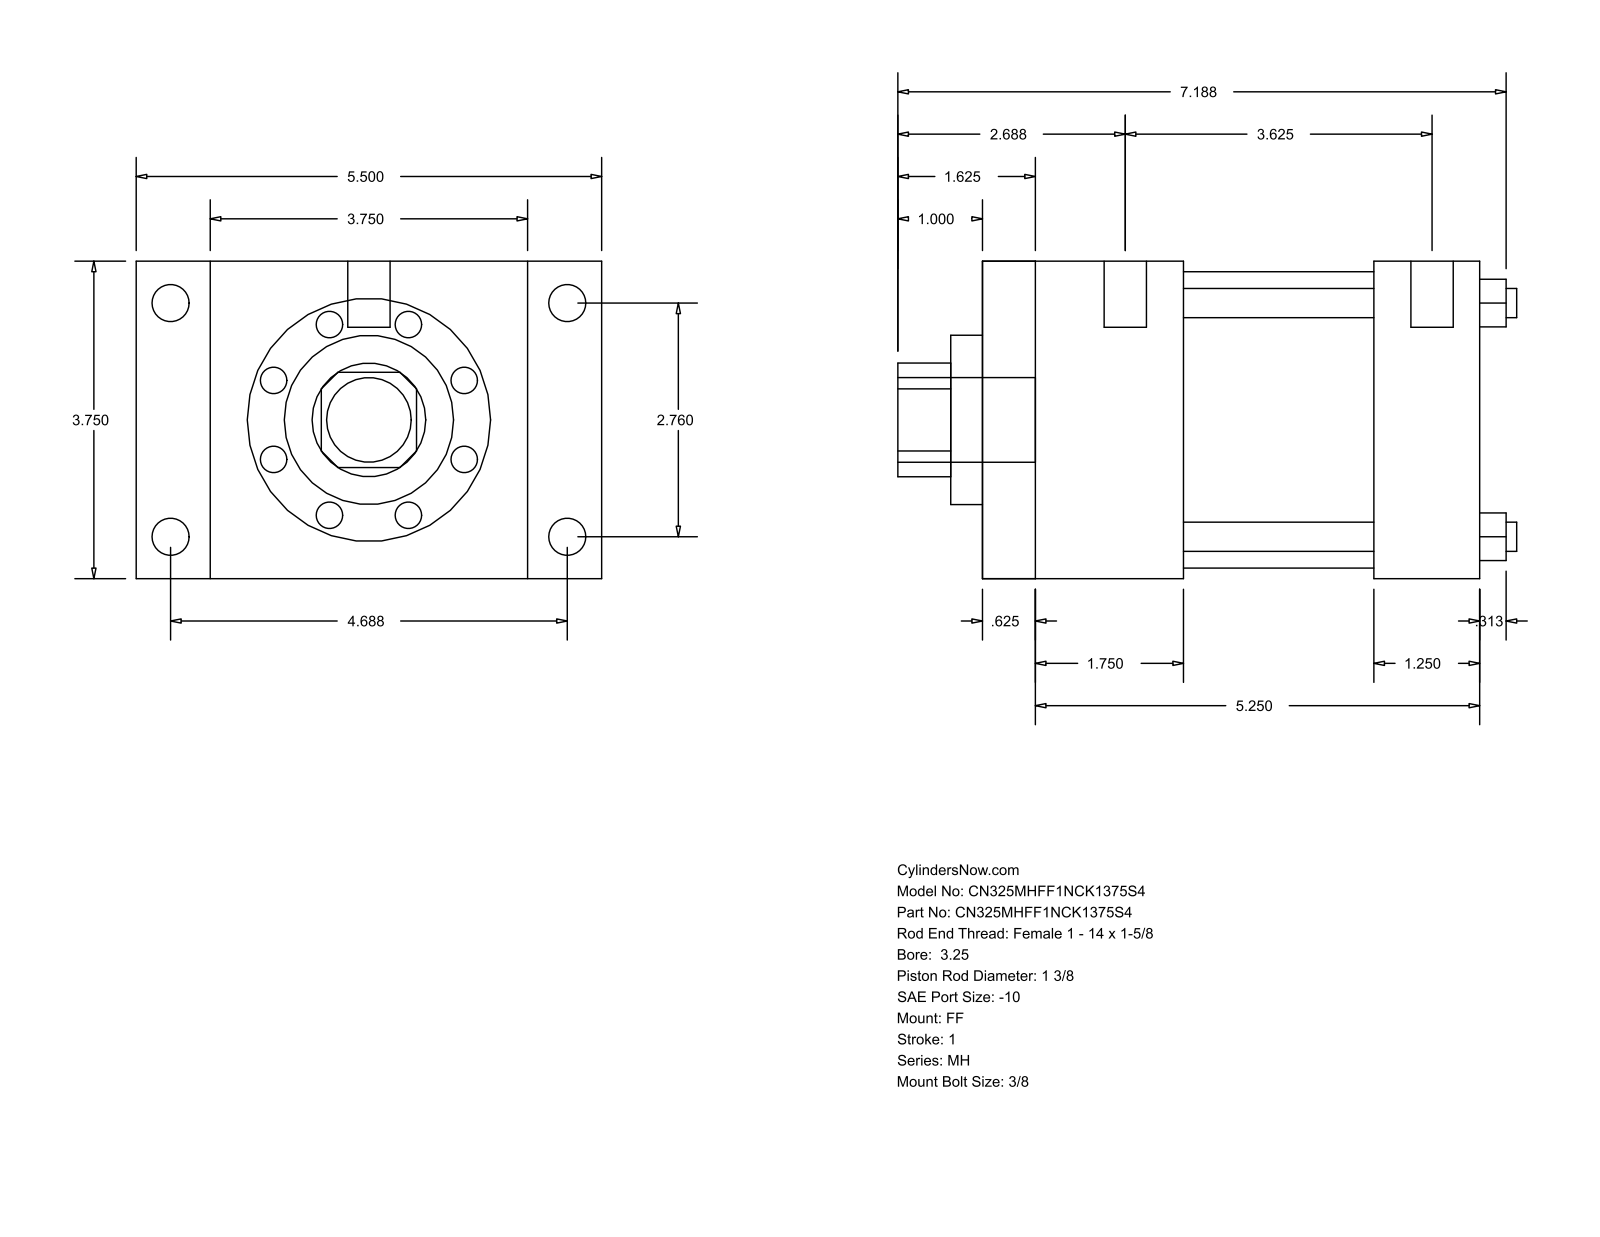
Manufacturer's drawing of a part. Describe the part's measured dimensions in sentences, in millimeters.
The part is named "MH_FF__0325_1.375". Its 3-D file was written by "GSSL Pune (CONFIG_CONTROL_DESIGN)". It is 0 solids with 92 faces: 64 planar, 28 cylindrical and 0 other. Overall it measures 185.74 by 139.7 by 95.25 millimeters. Round holes: 4 of diameter 8.76, 1 of diameter 34.92, 1 of diameter 50.8, 1 of diameter 88.9. Round bosses or shafts: 4 of diameter 11.13, 4 of diameter 5.56, 2 of diameter 12.7, 1 of diameter 25.4. Partial cylindrical surfaces (rounded edges, fillets, slot ends): 1 of radius 17.06. The main face-to-face distances are 95.24, 149.22, 15.87, 133.35, 22.23, 117.47, 117.48, 101.61, 31.74, 60.32. The hole center spacings are 49.57, 70.1, 99.14.
